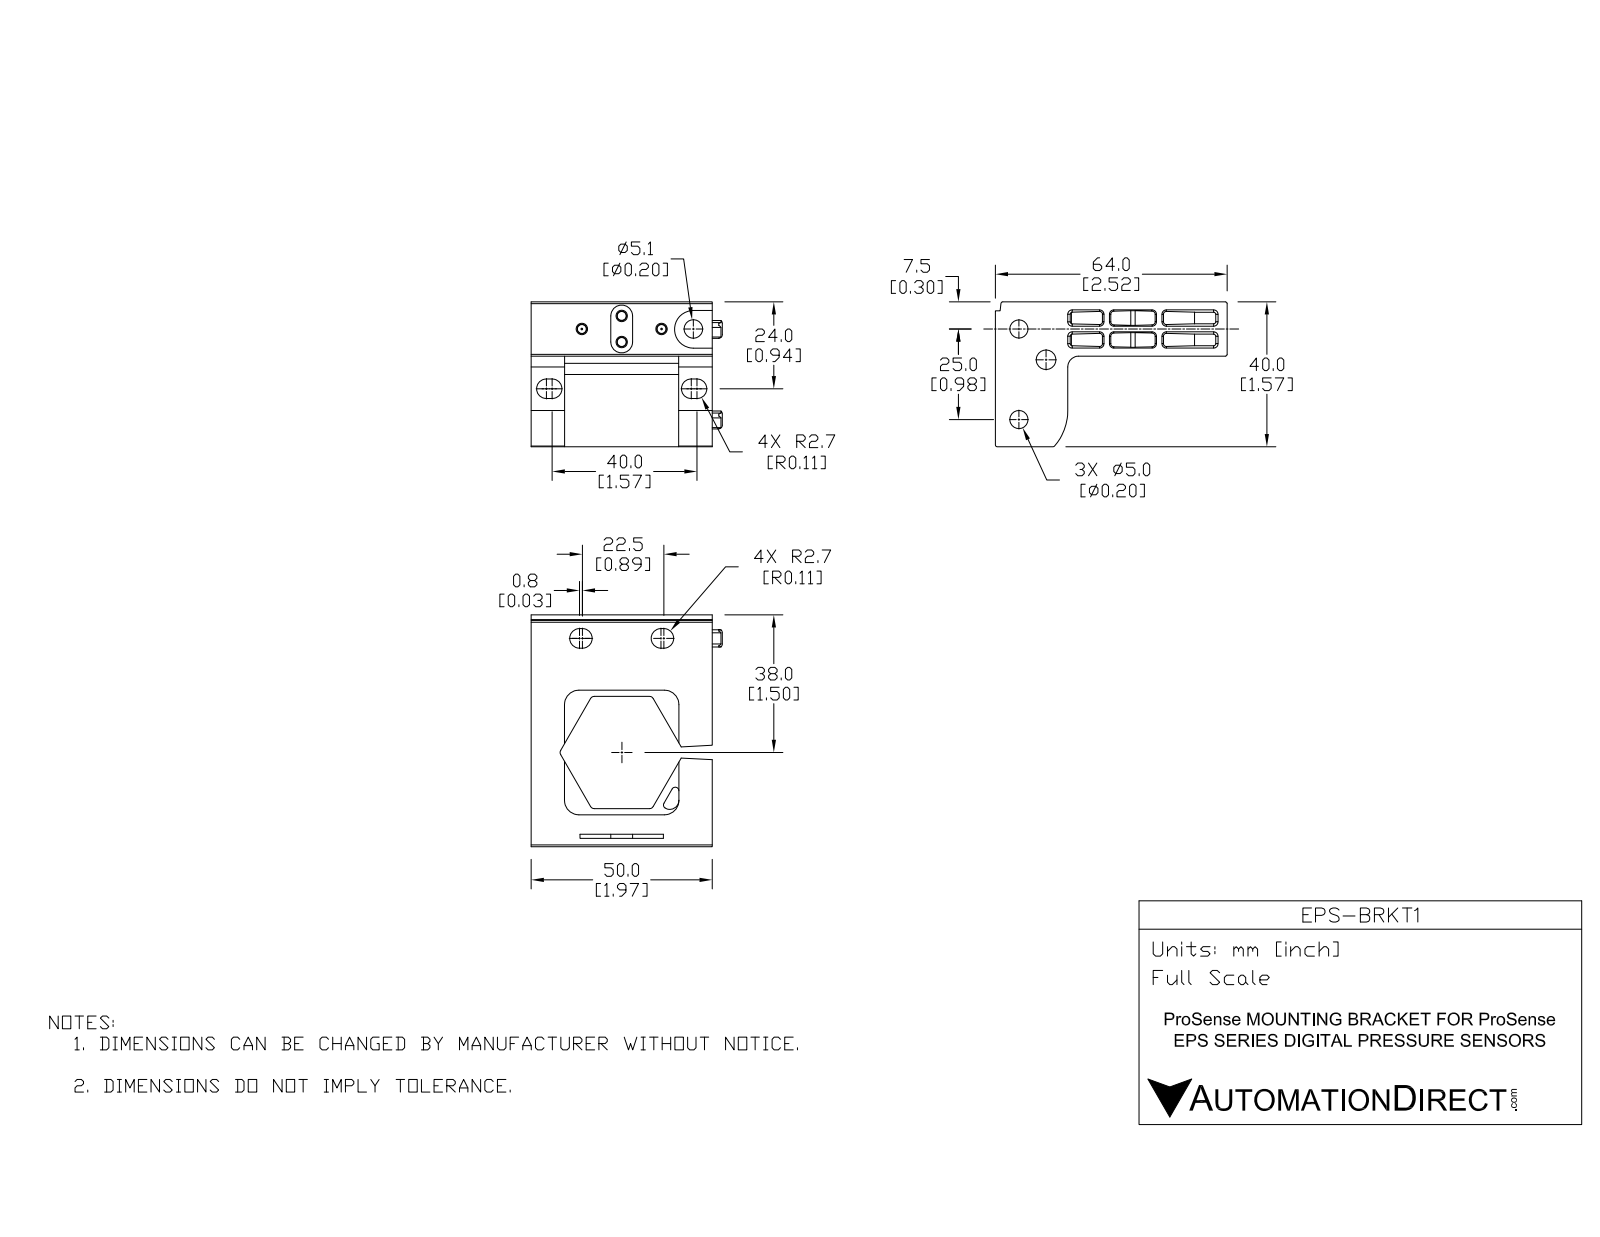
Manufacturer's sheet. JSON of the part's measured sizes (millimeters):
{"part_name": "EPS-BRKT1", "step_written_by": "SolidWorks 2016 (AUTOMOTIVE_DESIGN)", "units": "millimeters", "bodies": {"solids": 1, "faces": 437, "planar": 200, "cylindrical": 163, "other": 74}, "overall_size": [64, 51.8, 40], "volume_mm3": 29458, "surface_area_mm2": 25017, "round_holes": [[3.15, 4], [5, 2], [5.1, 1], [5.4, 1]], "partial_cylinders_radius": [[1.2, 46], [0.5, 13], [1, 8], [2.7, 8], [4, 8], [0.2, 4], [1.4, 4], [3, 3]], "face_to_face_distances": [15, 10, 40, 8.25, 17.5, 7.5, 1.54, 50, 22.5, 6.7], "hole_center_spacings": [11.57, 20.12, 7.2, 8.8, 11.34, 18.12, 22, 25]}
